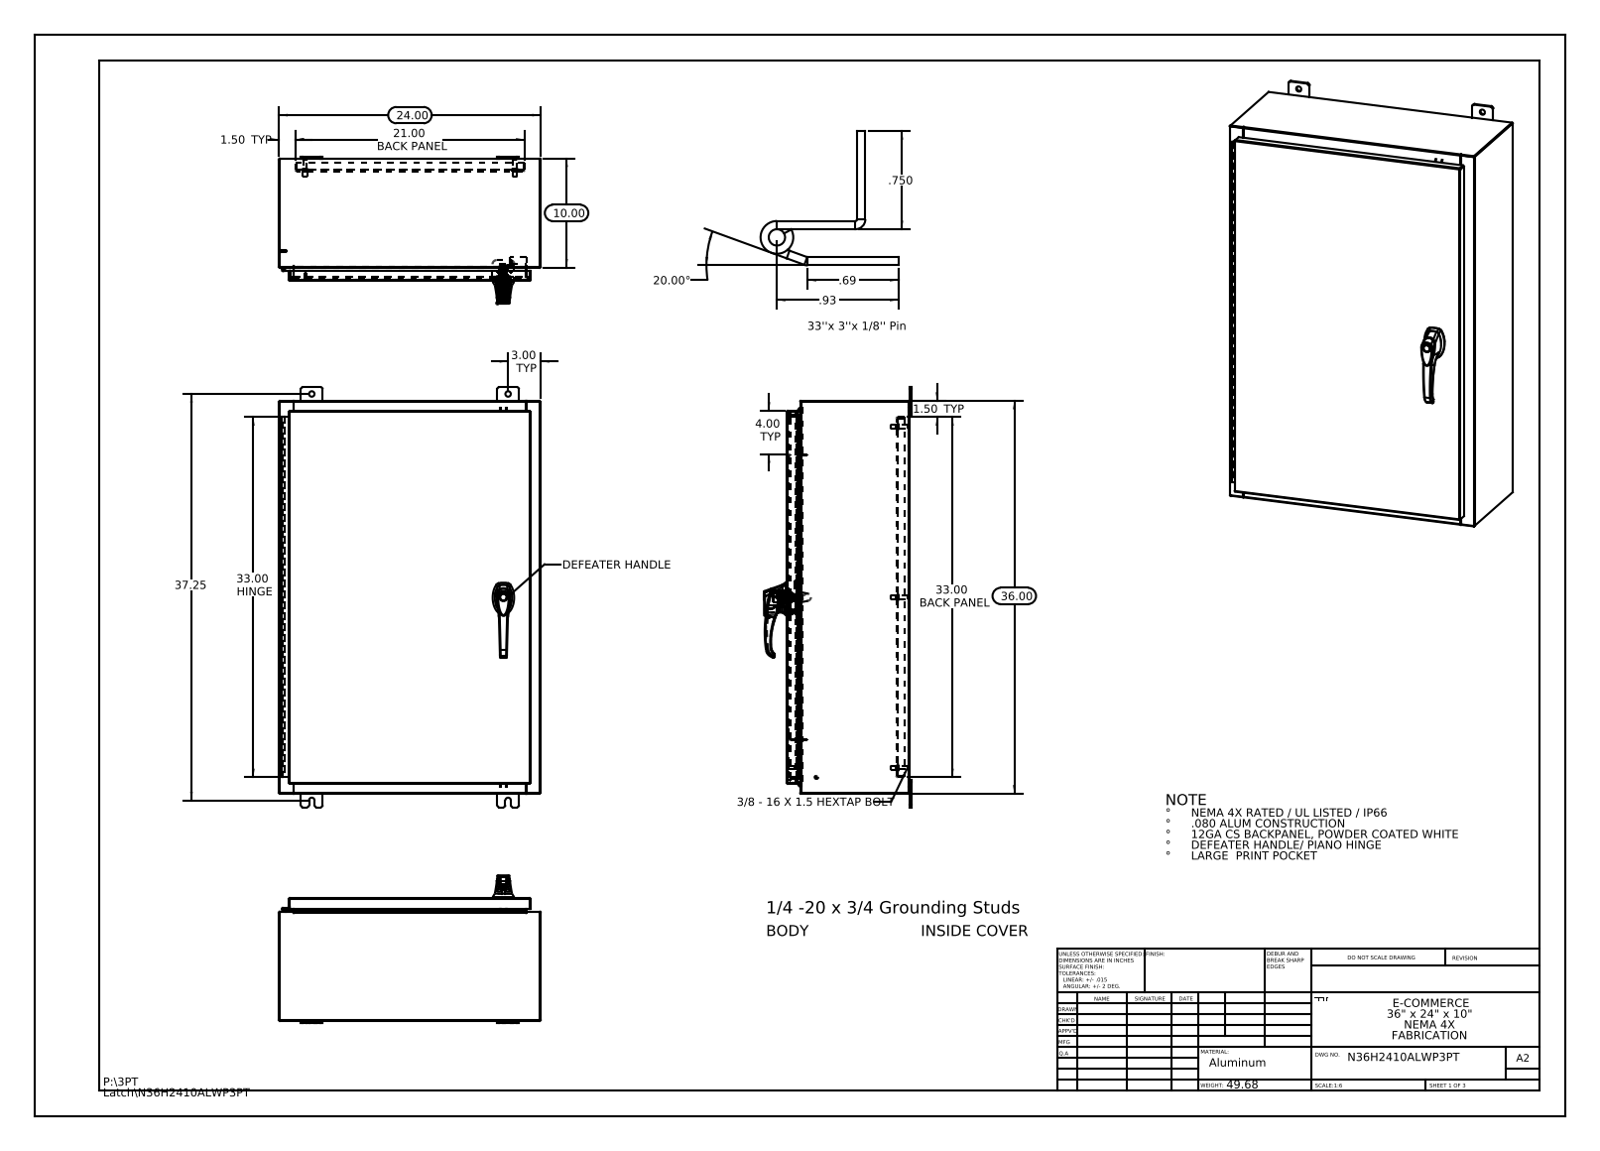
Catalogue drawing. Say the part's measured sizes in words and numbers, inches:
The part is named "g26103103_26163303; N36H2410ALWP3PT 125 Pin Hinge; N36H2410ALWP3PT Defeater Handle - 3 - 2500-51 ZN; N36H2410ALWP3PT Mounting Feet (+8 more)". Its 3-D file was written by "SolidWorks 2013 (CONFIG_CONTROL_DESIGN)". It is 39 solids with 2856 faces: 1053 planar, 1085 cylindrical and 718 other. Overall it measures 38.5 by 24 by 13.495 inches. Its volume is 336.4 cubic inches and its surface area 8 338 square inches. Round holes: 10 of diameter 0.5, 4 of diameter 0.25, 3 of diameter 0.138, 3 of diameter 0.161, 2 of diameter 0.079, 2 of diameter 0.203, 2 of diameter 0.313, 2 of diameter 0.437, 1 of diameter 0.125, 1 of diameter 0.125, 1 of diameter 0.197, 1 of diameter 0.276. Round bosses or shafts: 6 of diameter 0.625, 6 of diameter 0.375, 6 of diameter 0.33, 4 of diameter 0.157, 4 of diameter 0.14, 3 of diameter 0.315, 3 of diameter 0.236, 1 of diameter 1.181. Partial cylindrical surfaces (rounded edges, fillets, slot ends): 37 of radius 0.118, 33 of radius 0.006, 24 of radius 0.013, 24 of radius 0.19, 18 of radius 0.088, 15 of radius 0.039, 12 of radius 0.028, 6 of radius 0.008. The main face-to-face distances are 0.075, 11.126, 0.104, 11.051, 11.201, 23.925, 1, 1.075, 10.051, 10.126. The hole center spacings are 11.363, 13.669, 15.625, 24.793, 19.25, 0.295, 0.625, 0.841.
